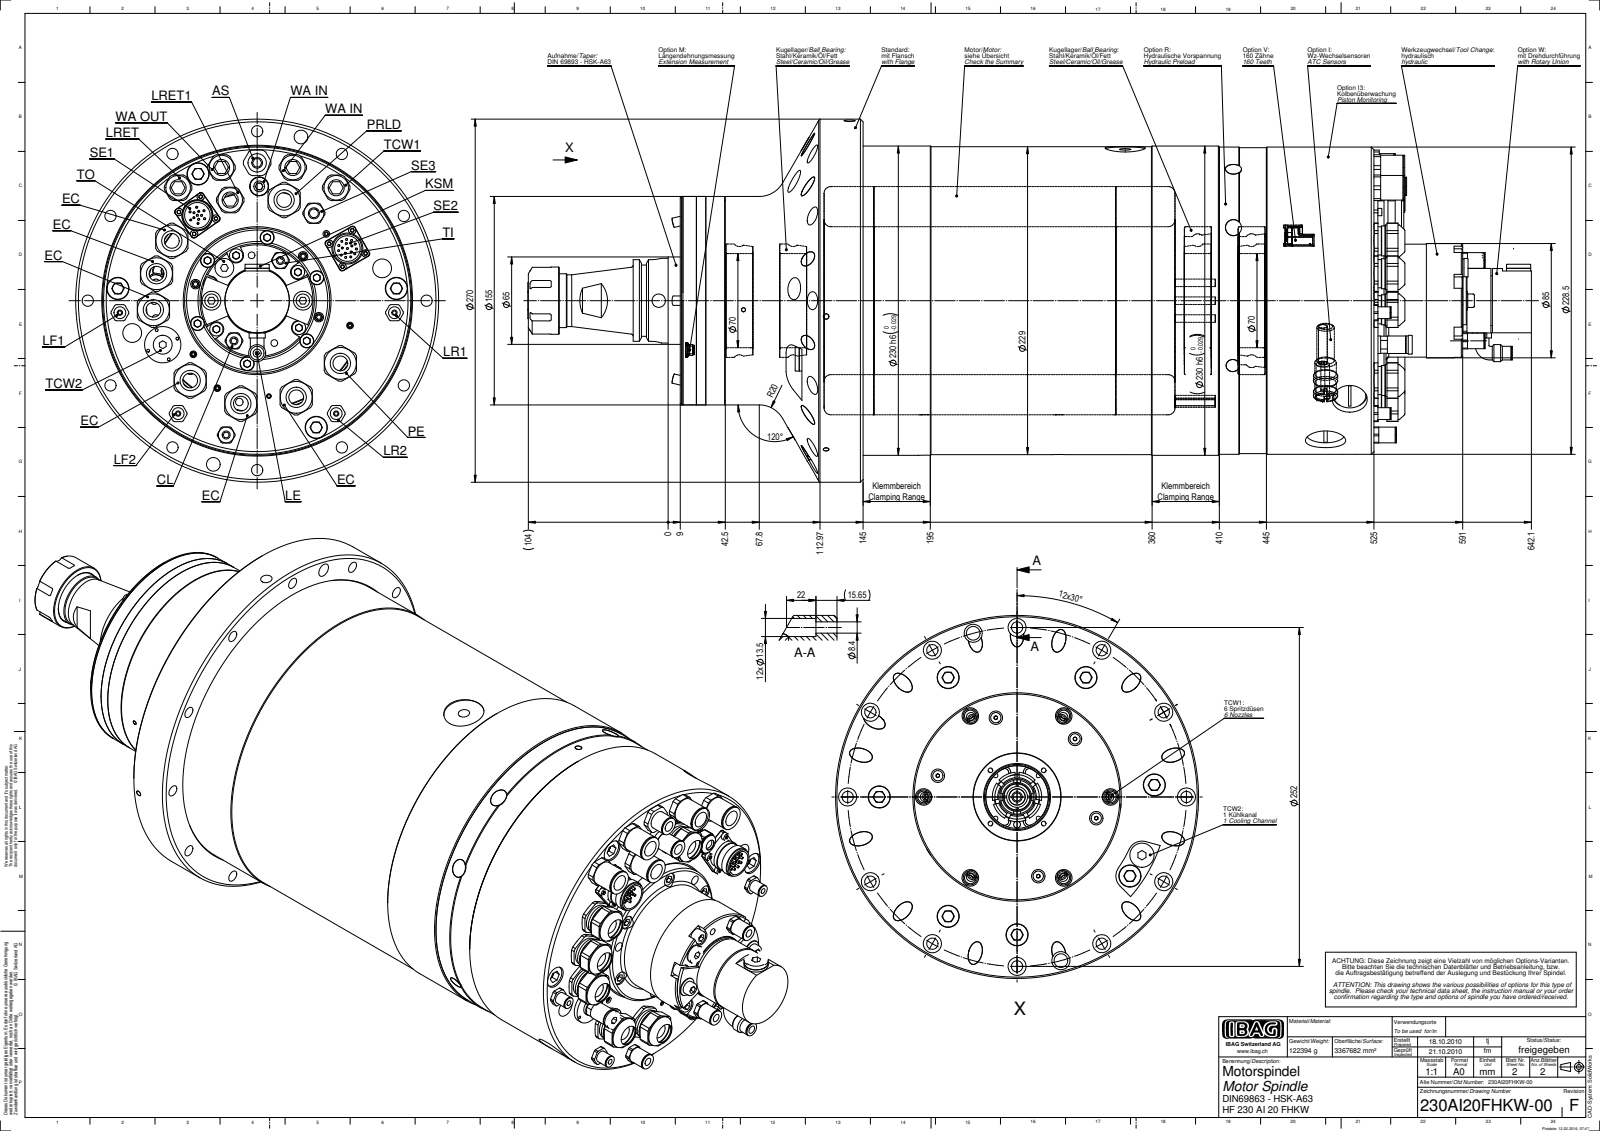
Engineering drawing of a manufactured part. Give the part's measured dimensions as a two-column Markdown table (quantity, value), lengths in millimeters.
| quantity | value |
| --- | --- |
| part name | 230AI20FHKW-00F |
| STEP written by | SolidWorks 2014 (CONFIG_CONTROL_DESIGN) |
| units | millimeters |
| bodies | 0 solids, 1836 faces (652 planar, 811 cylindrical, 373 other) |
| overall size | 746.46 × 270 × 270 |
| round holes (diameter × count) | 13.5 × 14, 5 × 12, 8.4 × 12, 16.5 × 11, 11 × 8, 15.1 × 8, 21.31 × 8, 10.4 × 6, 30 × 6, 10.5 × 5, 12 × 5, 4 × 4 |
| round bosses / shafts (diameter × count) | 1.5 × 28, 23.7 × 8, 22.3 × 8, 20.96 × 8, 10 × 8, 5.5 × 7, 7 × 6, 18.3 × 5 |
| partial cylindrical surfaces (radius × count) | 1 × 12, 13.2 × 8, 6.6 × 7, 10.25 × 6, 5.5 × 5, 8 × 4, 10.5 × 2, 8.25 × 1 |
| main face-to-face distances | 115, 35, 80, 382, 417, 497, 436, 19, 401, 516 |
| hole center spacings | 126, 65.22, 178.19, 218.24, 243.41, 63.35, 102.5, 116.05 |
